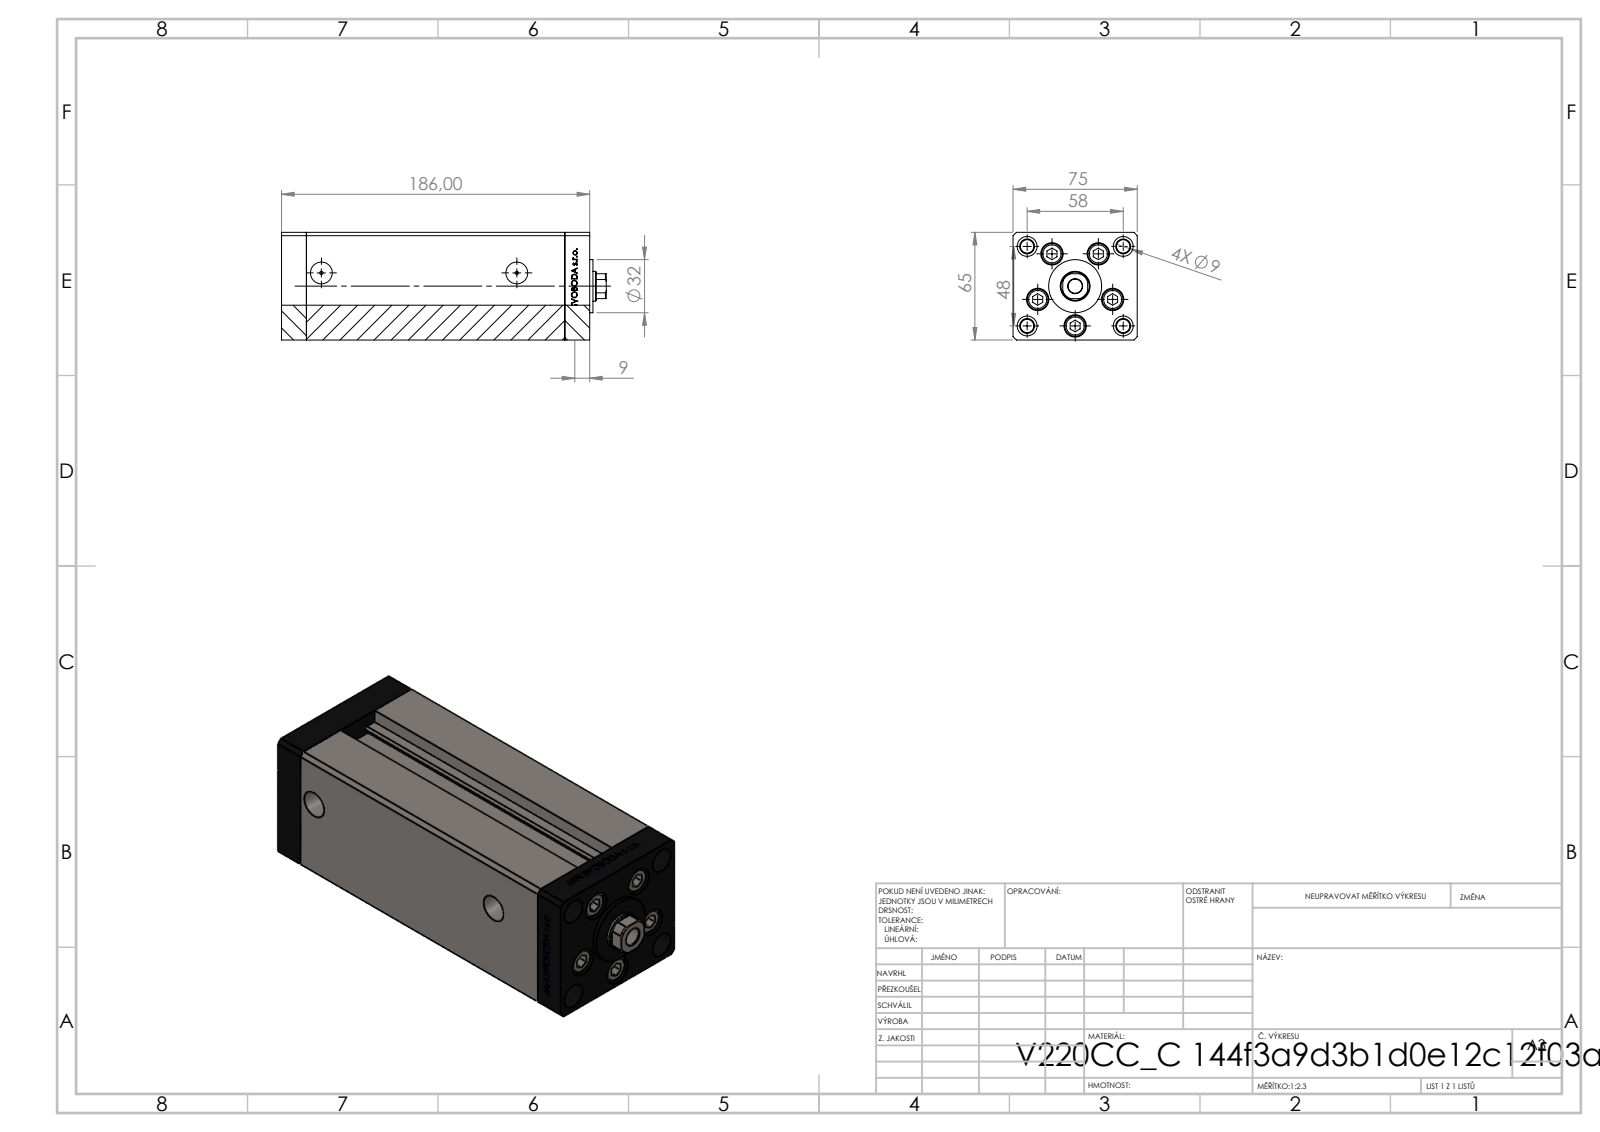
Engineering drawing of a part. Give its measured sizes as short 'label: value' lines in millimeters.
name: V220C BACK_C; V220C_C MIDDLE; V220C_VC_C; V220C FRONT (+1 more)
written by: SolidWorks 2019 (CONFIG_CONTROL_DESIGN)
unit: mm
bodies: 13 solids, 1169 faces (540 planar, 167 cylindrical, 462 other)
size: 196 × 75 × 65
volume: 757 889 mm³; area: 153 912 mm²
holes: 9× ⌀9, 5× ⌀13.5, 4× ⌀8, 4× ⌀12, 2× ⌀2, 2× ⌀13.16, 1× ⌀8.5, 1× ⌀12.5, 1× ⌀18
bosses: 5× ⌀8, 4× ⌀12.5, 1× ⌀32
rounds: 2× R0.93, 1× R8.5
face distances: 75, 65, 15, 156, 171, 186, 28, 54.5, 10.5, 26.25
hole spacings: 24, 37.64, 15.67, 17.22, 27.71, 28.83, 29, 32.63
